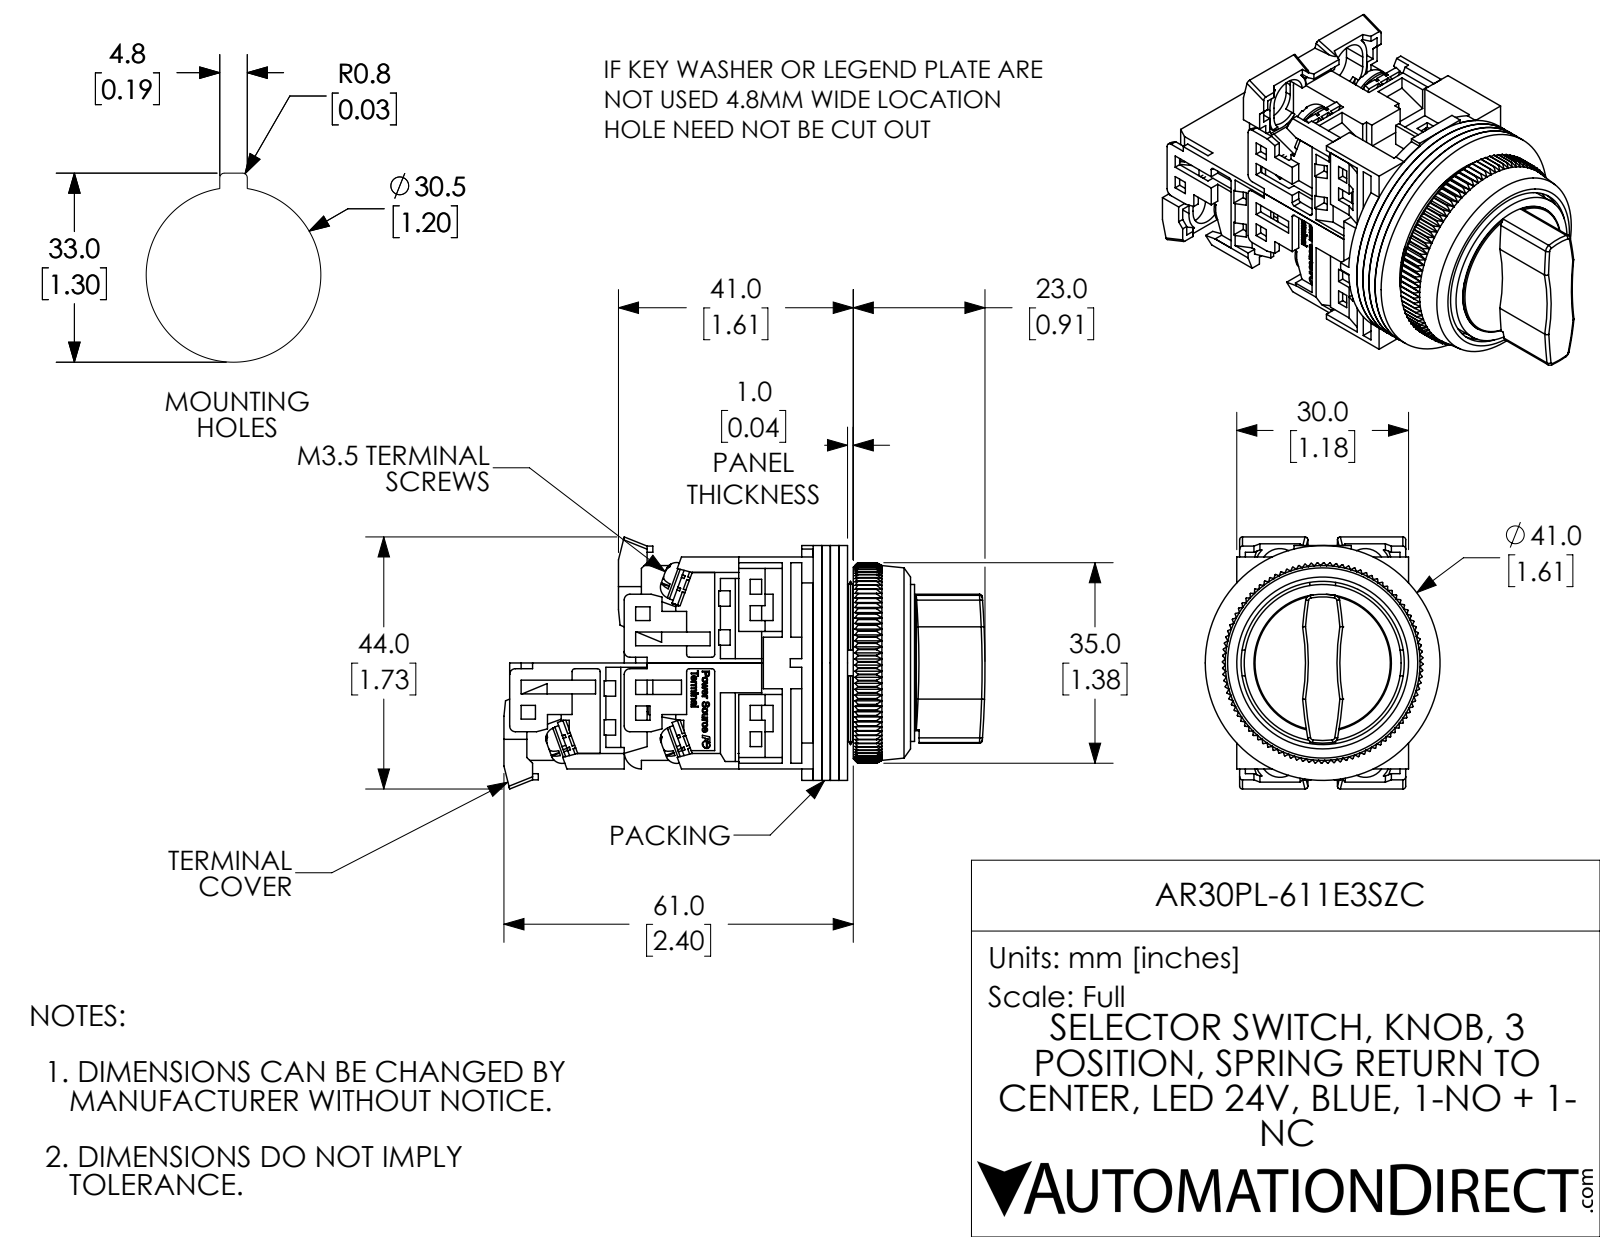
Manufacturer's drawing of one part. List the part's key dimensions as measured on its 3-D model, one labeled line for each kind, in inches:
Part name (STEP PRODUCT): AR30PL-611E3SZC
STEP written by: SolidWorks 2017 (AUTOMOTIVE_DESIGN)
Units: inches
Bodies: 32 solids, 2783 faces (2039 planar, 338 cylindrical, 406 other)
Overall size (bounding box): 3.307 × 1.732 × 1.614
Volume: 2.677 in³ · Surface area: 66.54 in²
Round holes (diameter × count): ⌀0.138 ×10, ⌀0.142 ×6, ⌀0.118 ×1, ⌀0.472 ×1, ⌀0.709 ×1, ⌀0.768 ×1, ⌀0.827 ×1, ⌀1.122 ×1, ⌀1.181 ×1, ⌀1.252 ×1
Round bosses / shafts (diameter × count): ⌀0.26 ×6, ⌀0.138 ×6, ⌀0.063 ×2, ⌀1.614 ×1, ⌀1.15 ×1, ⌀1.079 ×1, ⌀0.945 ×1, ⌀0.886 ×1
Partial cylindrical surfaces — rounded edges, fillets, slot ends (radius × count): R0.059 ×24, R0.02 ×14, R0.039 ×10, R0.138 ×4, R0.177 ×4, R0.118 ×3, R1.575 ×2, R2.953 ×2
Main face-to-face distances: 0.059, 0.118, 0.177, 0.039, 0.787, 0.063, 0.079, 0.02, 0.811, 0.689
Hole centre spacings: 0.579, 0.269, 0.638, 0.61
